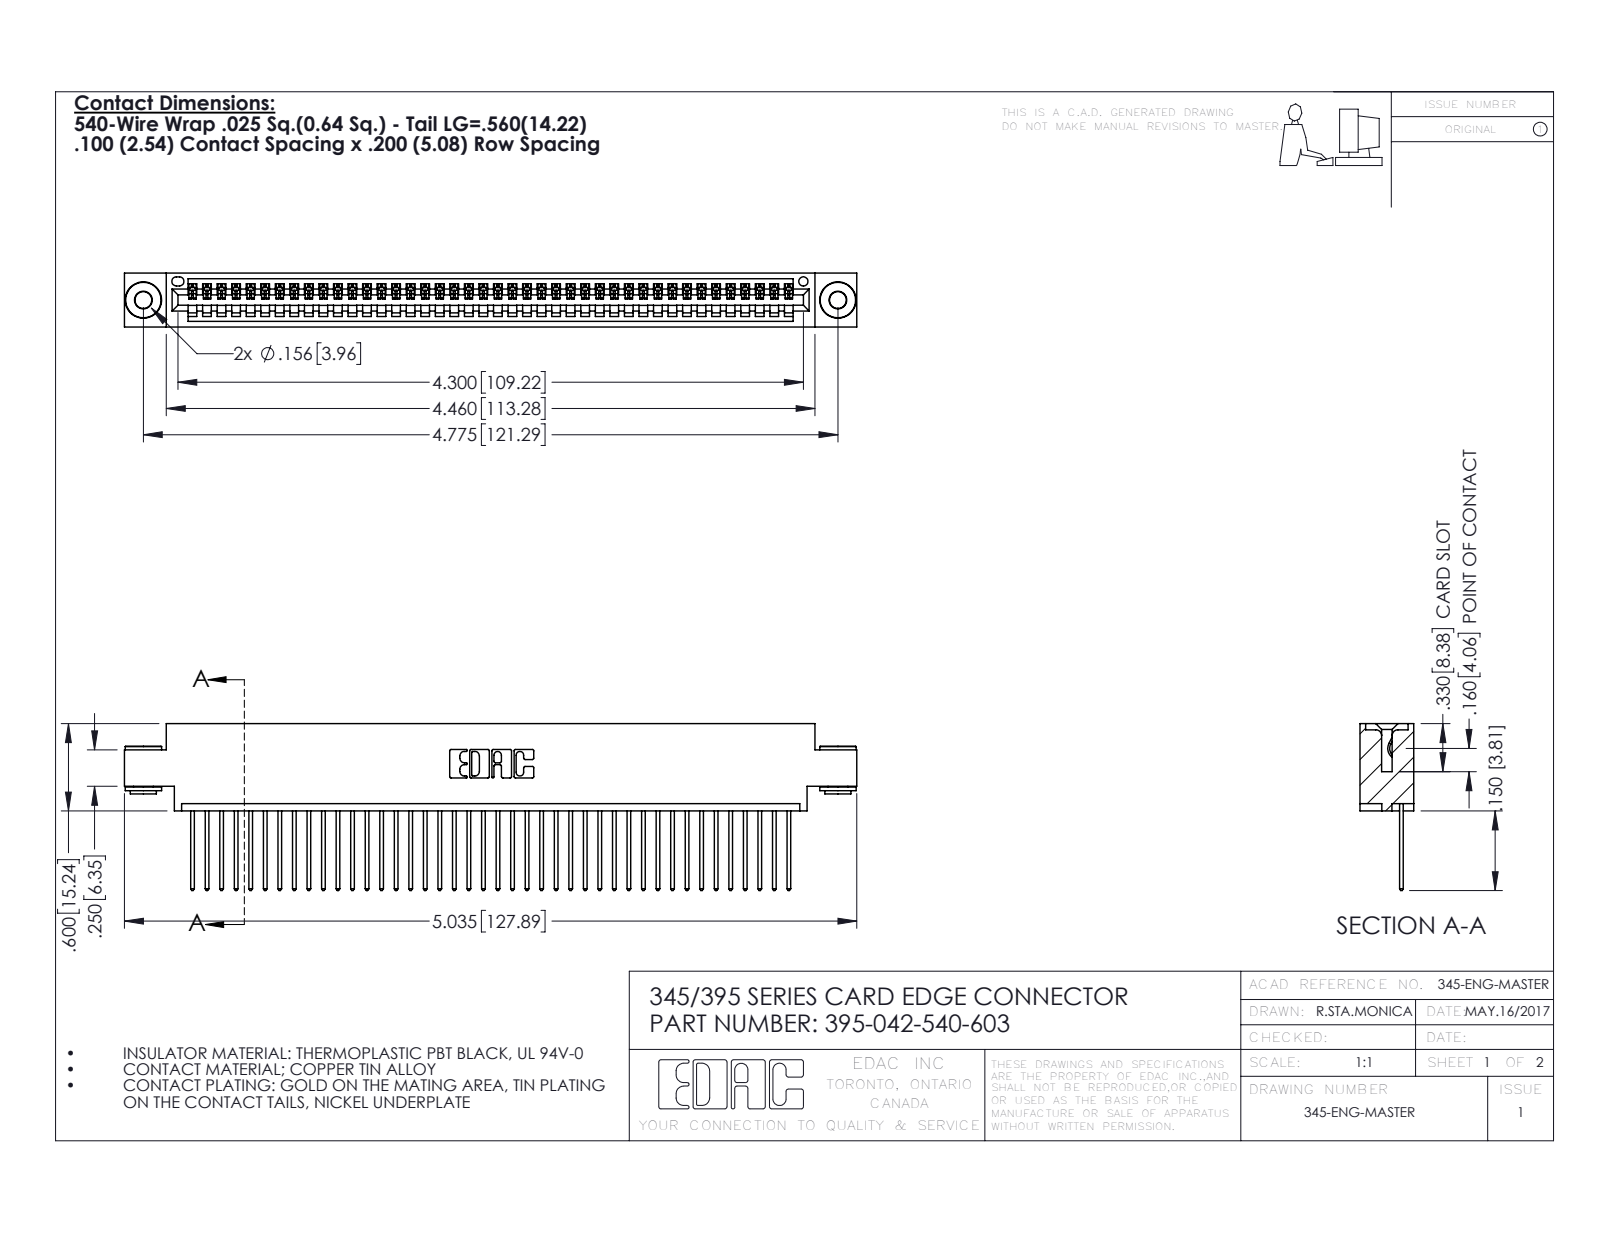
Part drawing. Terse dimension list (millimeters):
name: 395-042-540-603; 345 Part_0.170 Offset - 0.156 Dia-TH; 345-250-002_345-250-002-102; 345-292-001_345-293-140
written by: SolidWorks 2016 (CONFIG_CONTROL_DESIGN)
unit: mm
bodies: 45 solids, 2604 faces (1774 planar, 822 cylindrical, 8 other)
size: 127.9 × 29.1 × 9.4
volume: 12 100 mm³; area: 16 850 mm²
holes: 2× ⌀2.9, 2× ⌀4, 1× ⌀1.6
bosses: 2× ⌀6.4, 2× ⌀4.6, 2× ⌀3.5
rounds: 84× R0.2, 84× R0.3, 22× R0.3, 6× R0.2, 6× R0.8, 3× R0.7, 2× R0.8, 2× R1
face distances: 1.8, 7.6, 9.4, 2.5, 6.9, 0.6, 5.1, 5.7, 4.4, 3.8
hole spacings: 6.9, 115.3, 121.3
